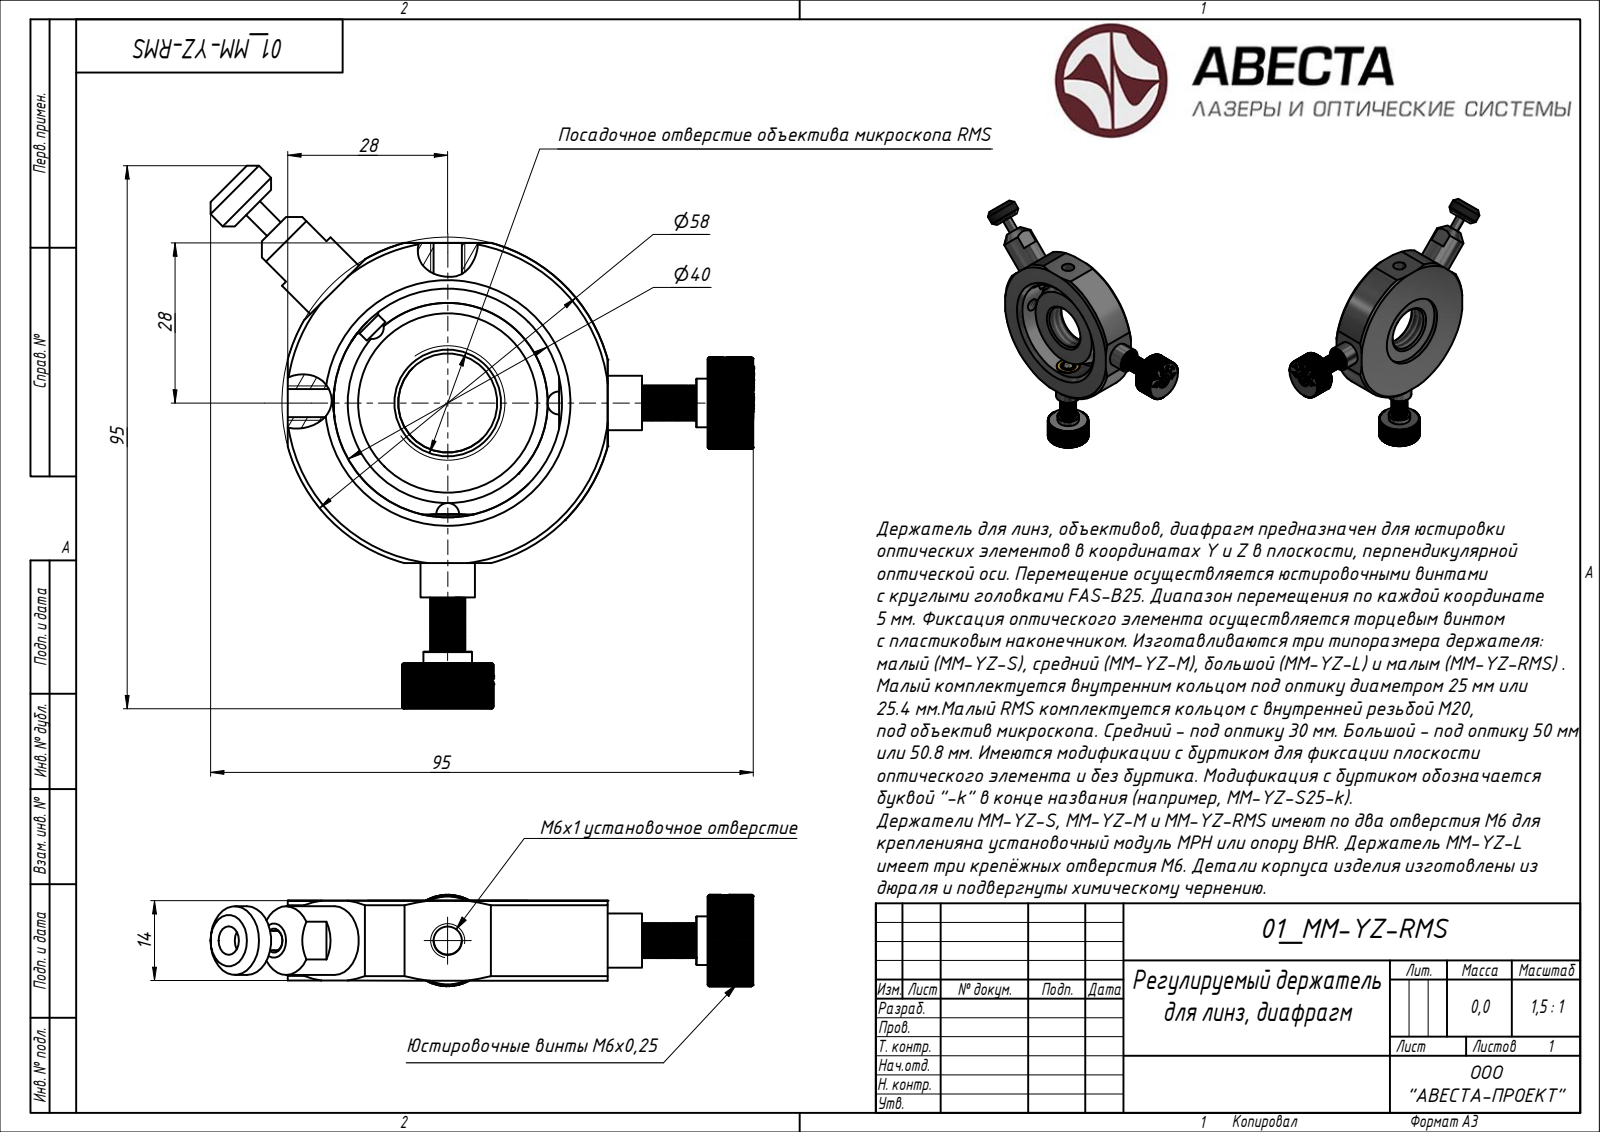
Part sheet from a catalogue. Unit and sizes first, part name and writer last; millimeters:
Units: millimetres
Overall size (bounding box): 96.78 × 85.14 × 16.02
Main face-to-face distances: 14, 12.52, 1.48, 1.5, 12.5, 7.99, 9.49, 4.51, 8.01, 8
Volume: 31 286 mm³ · Surface area: 19 071 mm²
Bodies: 14 solids, 578 faces (263 planar, 0 cylindrical, 315 other)
STEP written by: ST-DEVELOPER v15 (AUTOMOTIVE_DESIGN)
